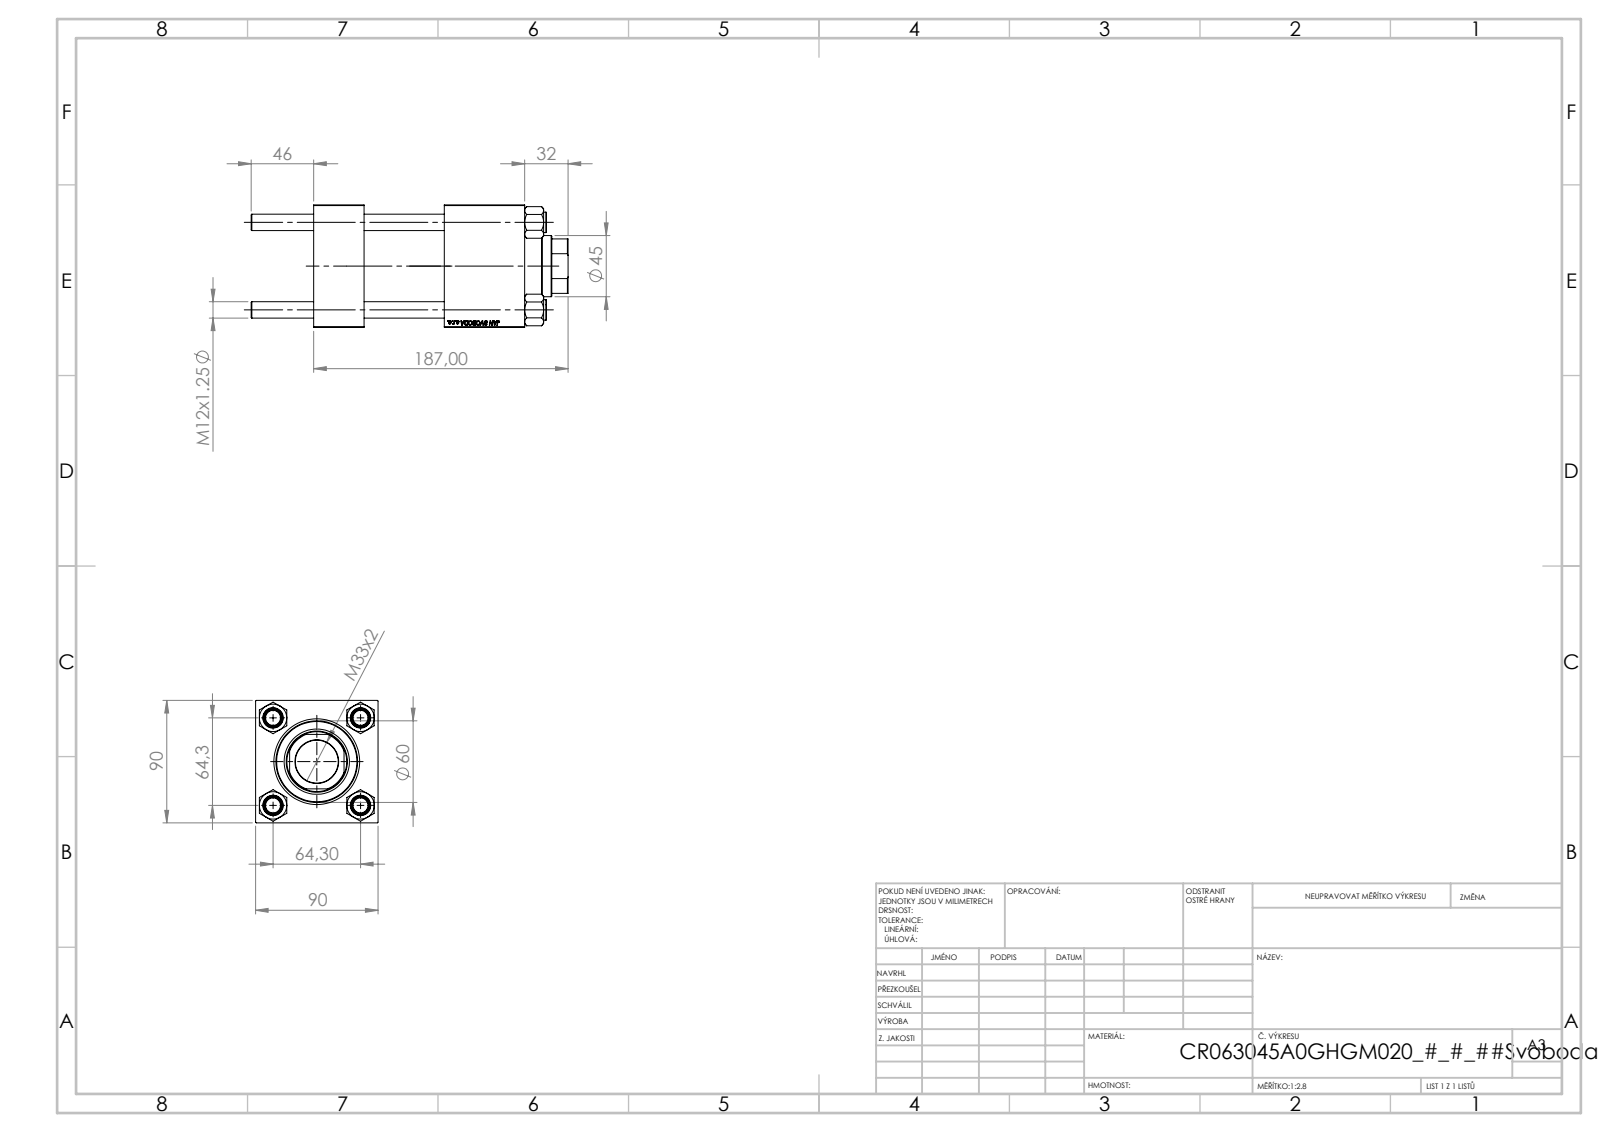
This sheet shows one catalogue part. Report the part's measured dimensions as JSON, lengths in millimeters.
{"part_name": "V215CR_VCP; V215CR_BODY_A; NUT_M5; V215_VC_A (+1 more)", "step_written_by": "SolidWorks 2019 (CONFIG_CONTROL_DESIGN)", "units": "millimeters", "bodies": {"solids": 11, "faces": 1131, "planar": 519, "cylindrical": 76, "other": 536}, "overall_size": [233, 90, 90], "volume_mm3": 1032000, "surface_area_mm2": 206066, "round_holes": [[12, 4], [7, 2], [20.96, 2], [30, 2], [31.5, 1], [45, 1], [48, 1], [50, 1], [60, 1], [63, 1]], "round_bosses_or_shafts": [[15, 4], [69, 1]], "partial_cylinders_radius": [[22, 1]], "face_to_face_distances": [90, 59, 37, 155, 118, 96, 126.3, 89.3, 30.3, 28.7], "hole_center_spacings": [45.47, 64.3, 90.93, 97.5]}
